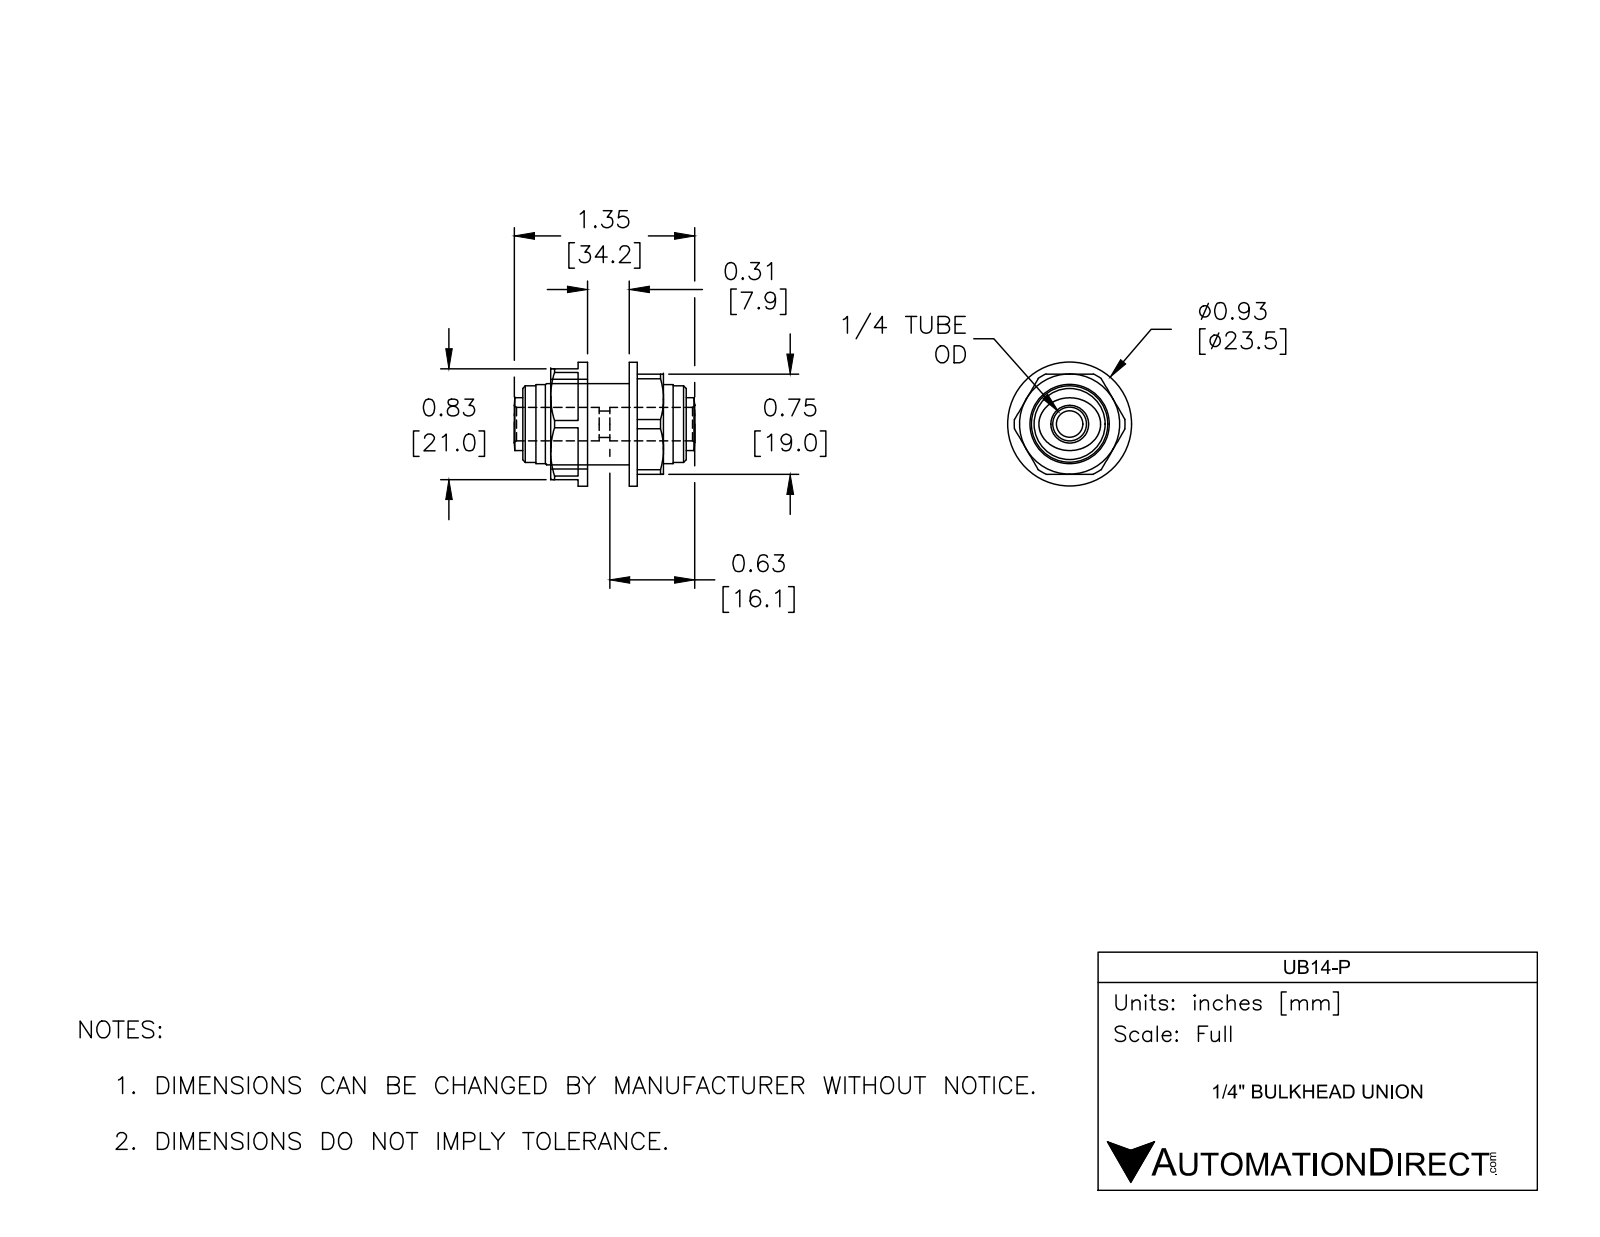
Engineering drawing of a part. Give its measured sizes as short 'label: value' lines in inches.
name: UB14-P
written by: SolidWorks 2017 (AUTOMOTIVE_DESIGN)
unit: in
bodies: 1 solid, 93 faces (31 planar, 30 cylindrical, 32 other)
size: 1.346 × 0.925 × 0.925
volume: 0.458 in³; area: 6.1 in²
holes: 1× ⌀0.197, 1× ⌀0.25
bosses: 1× ⌀0.925, 1× ⌀0.669, 1× ⌀0.591, 1× ⌀0.571
rounds: 1× R0.413
face distances: 0.039, 0.787, 0.311, 0.827, 0.071, 0.748, 0.059, 0.37, 0.646, 0.587
